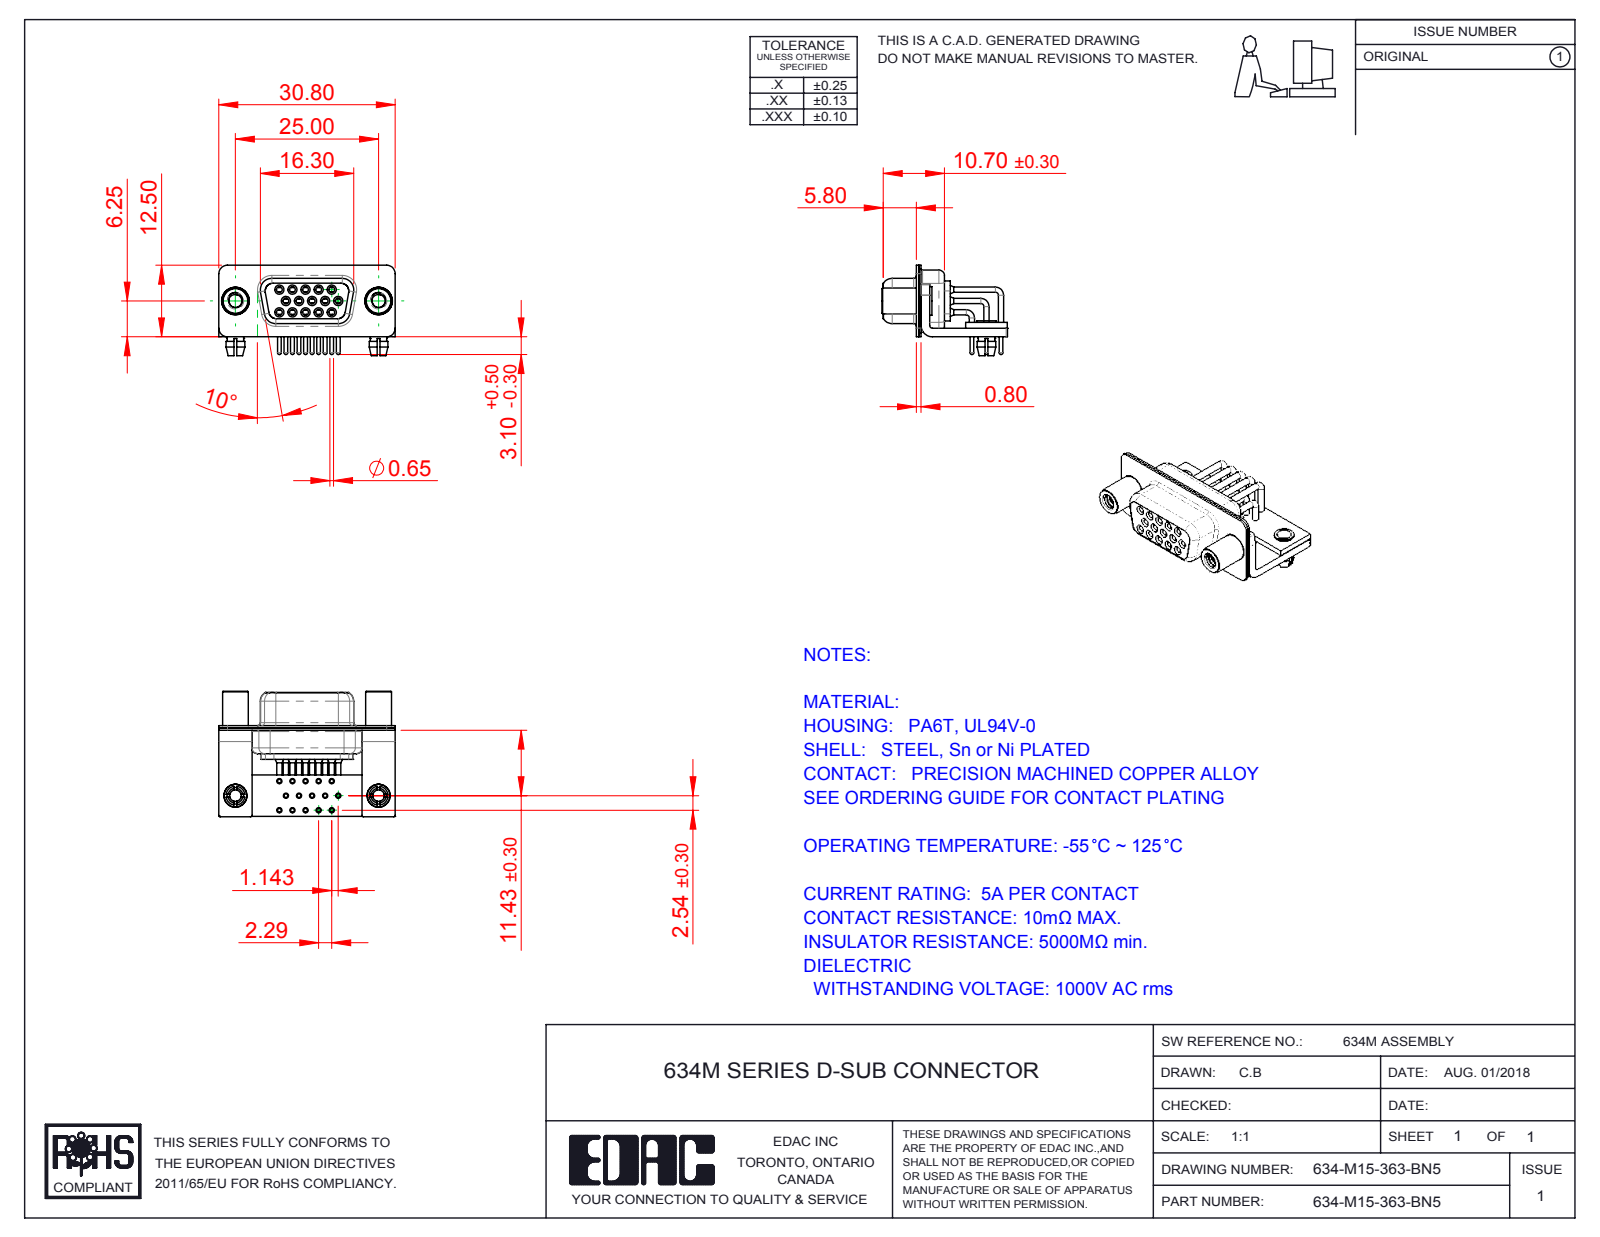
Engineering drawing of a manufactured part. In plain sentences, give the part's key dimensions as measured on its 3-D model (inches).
The part is named "634M Board Lock; 634-M15-363-BN5; 634M Contact Row 3; 634M Contact Row 2 (+7 more)". Its 3-D file was written by "SolidWorks 2016 (CONFIG_CONTROL_DESIGN)". It is 25 solids with 1296 faces: 368 planar, 608 cylindrical and 320 other. Overall it measures 1.213 by 0.862 by 0.622 inches. Its volume is 0.146 cubic inches and its surface area 11.44 square inches. Round holes: 17 of diameter 0.079, 15 of diameter 0.035, 15 of diameter 0.039, 15 of diameter 0.043, 15 of diameter 0.067, 15 of diameter 0.071, 2 of diameter 0.089, 2 of diameter 0.098, 2 of diameter 0.126, 2 of diameter 0.157, 2 of diameter 0.189. Round bosses or shafts: 15 of diameter 0.063, 15 of diameter 0.059, 15 of diameter 0.035, 15 of diameter 0.026, 2 of diameter 0.197, 2 of diameter 0.193, 2 of diameter 0.177, 2 of diameter 0.157. Partial cylindrical surfaces (rounded edges, fillets, slot ends): 16 of radius 0.01, 16 of radius 0.059, 13 of radius 0.079, 8 of radius 0.053, 8 of radius 0.063, 5 of radius 0.02, 4 of radius 0.024, 4 of radius 0.026. The main face-to-face distances are 0.016, 0.059, 0.031, 0.091, 0.075, 0.039, 0.368, 0.335, 0.057, 0.098. The hole center spacings are 0.09, 0.09, 0.18, 0.156, 0.168, 0.109, 0.238, 0.27.
